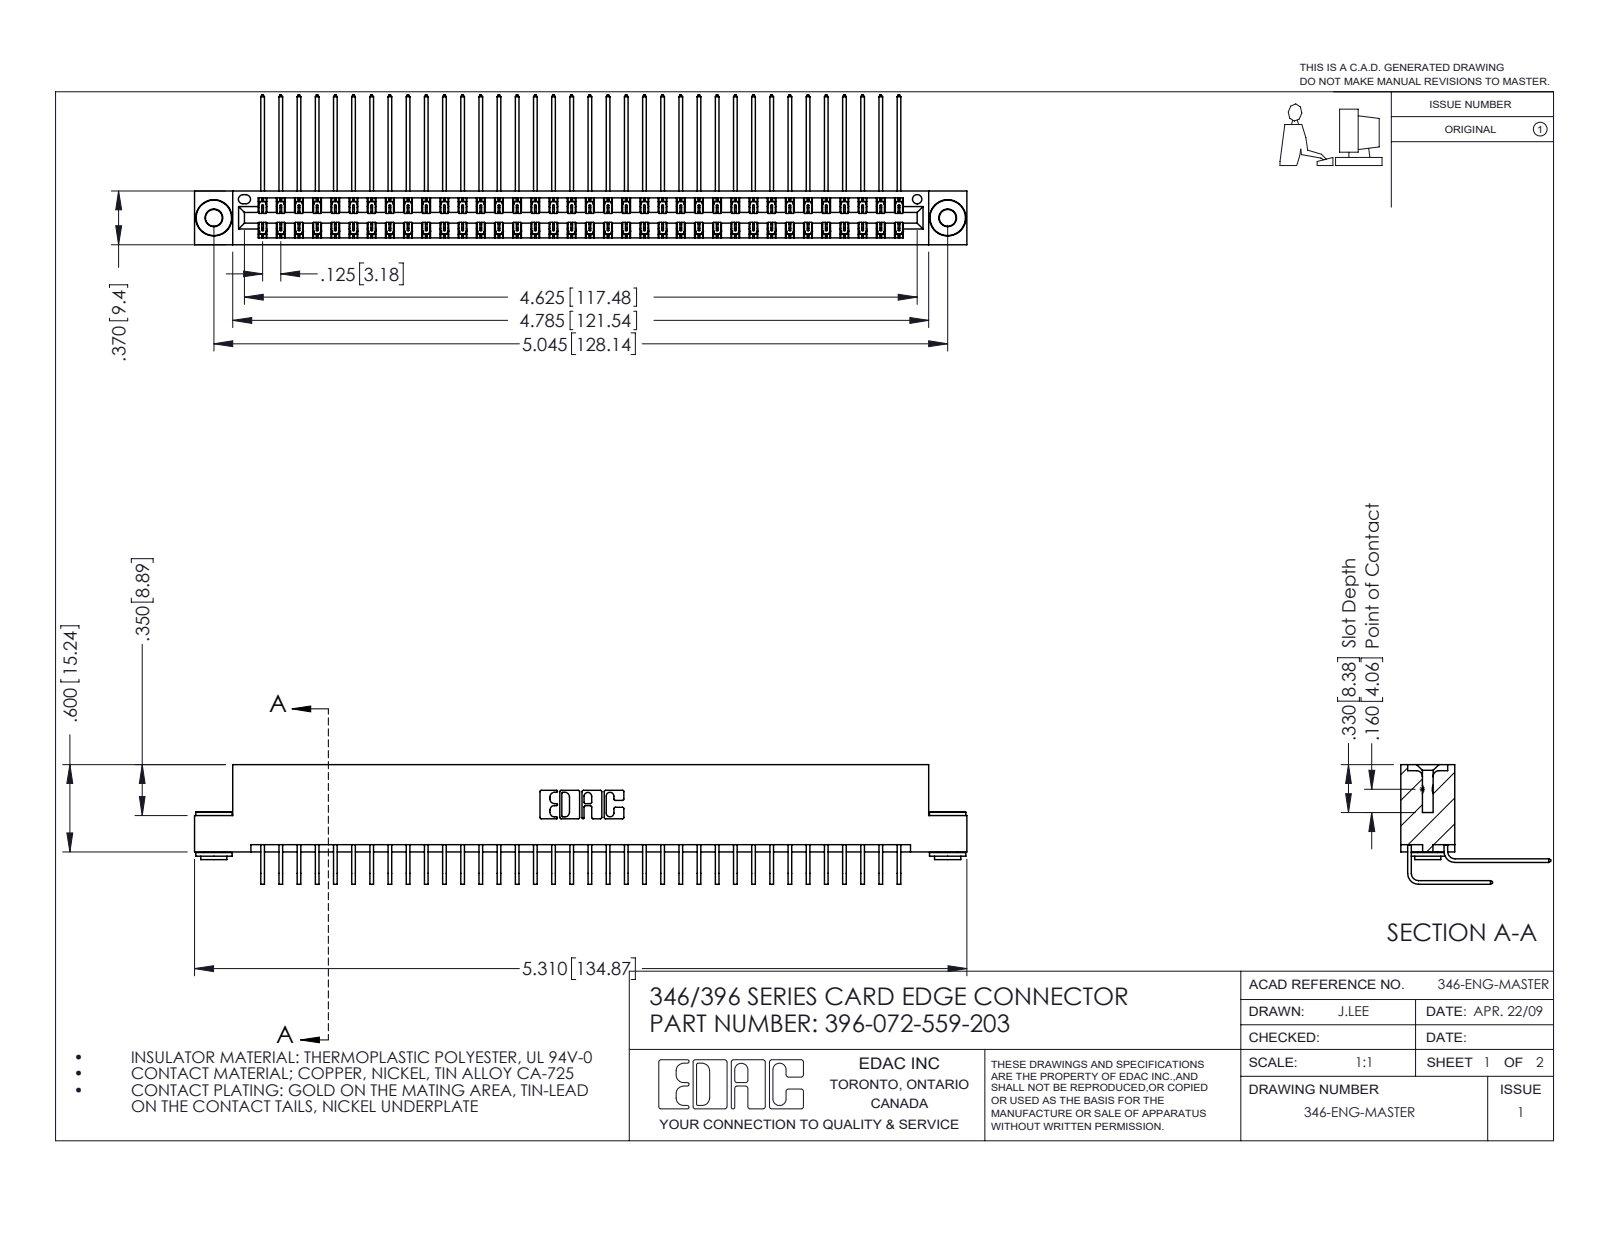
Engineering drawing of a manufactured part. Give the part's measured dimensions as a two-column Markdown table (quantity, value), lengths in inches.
| quantity | value |
| --- | --- |
| part name | 345-292-001_558 559 Tail - 1; 346 Part_Flush Mounting Lugs - 0.156 Dia-TH; 396-072-559-203; 345-292-001_559 Tail - 2 (+1 more) |
| STEP written by | SolidWorks 2016 (CONFIG_CONTROL_DESIGN) |
| units | inches |
| bodies | 75 solids, 4048 faces (2750 planar, 1290 cylindrical, 8 other) |
| overall size | 5.31 × 1.03 × 0.823 |
| volume | 0.826 in³ |
| surface area | 32.12 in² |
| round holes (diameter × count) | 0.116 × 2, 0.156 × 2, 0.064 × 1 |
| round bosses / shafts (diameter × count) | 0.25 × 2, 0.18 × 2, 0.136 × 2 |
| partial cylindrical surfaces (radius × count) | 0.006 × 108, 0.01 × 22, 0.007 × 6, 0.031 × 6, 0.026 × 3, 0.014 × 2, 0.022 × 2, 0.024 × 2 |
| main face-to-face distances | 0.048, 0.322, 0.025, 0.25, 0.37, 0.072, 0.298, 0.275, 0.148, 0.222 |
| hole center spacings | 0.246, 4.836, 5.045 |
